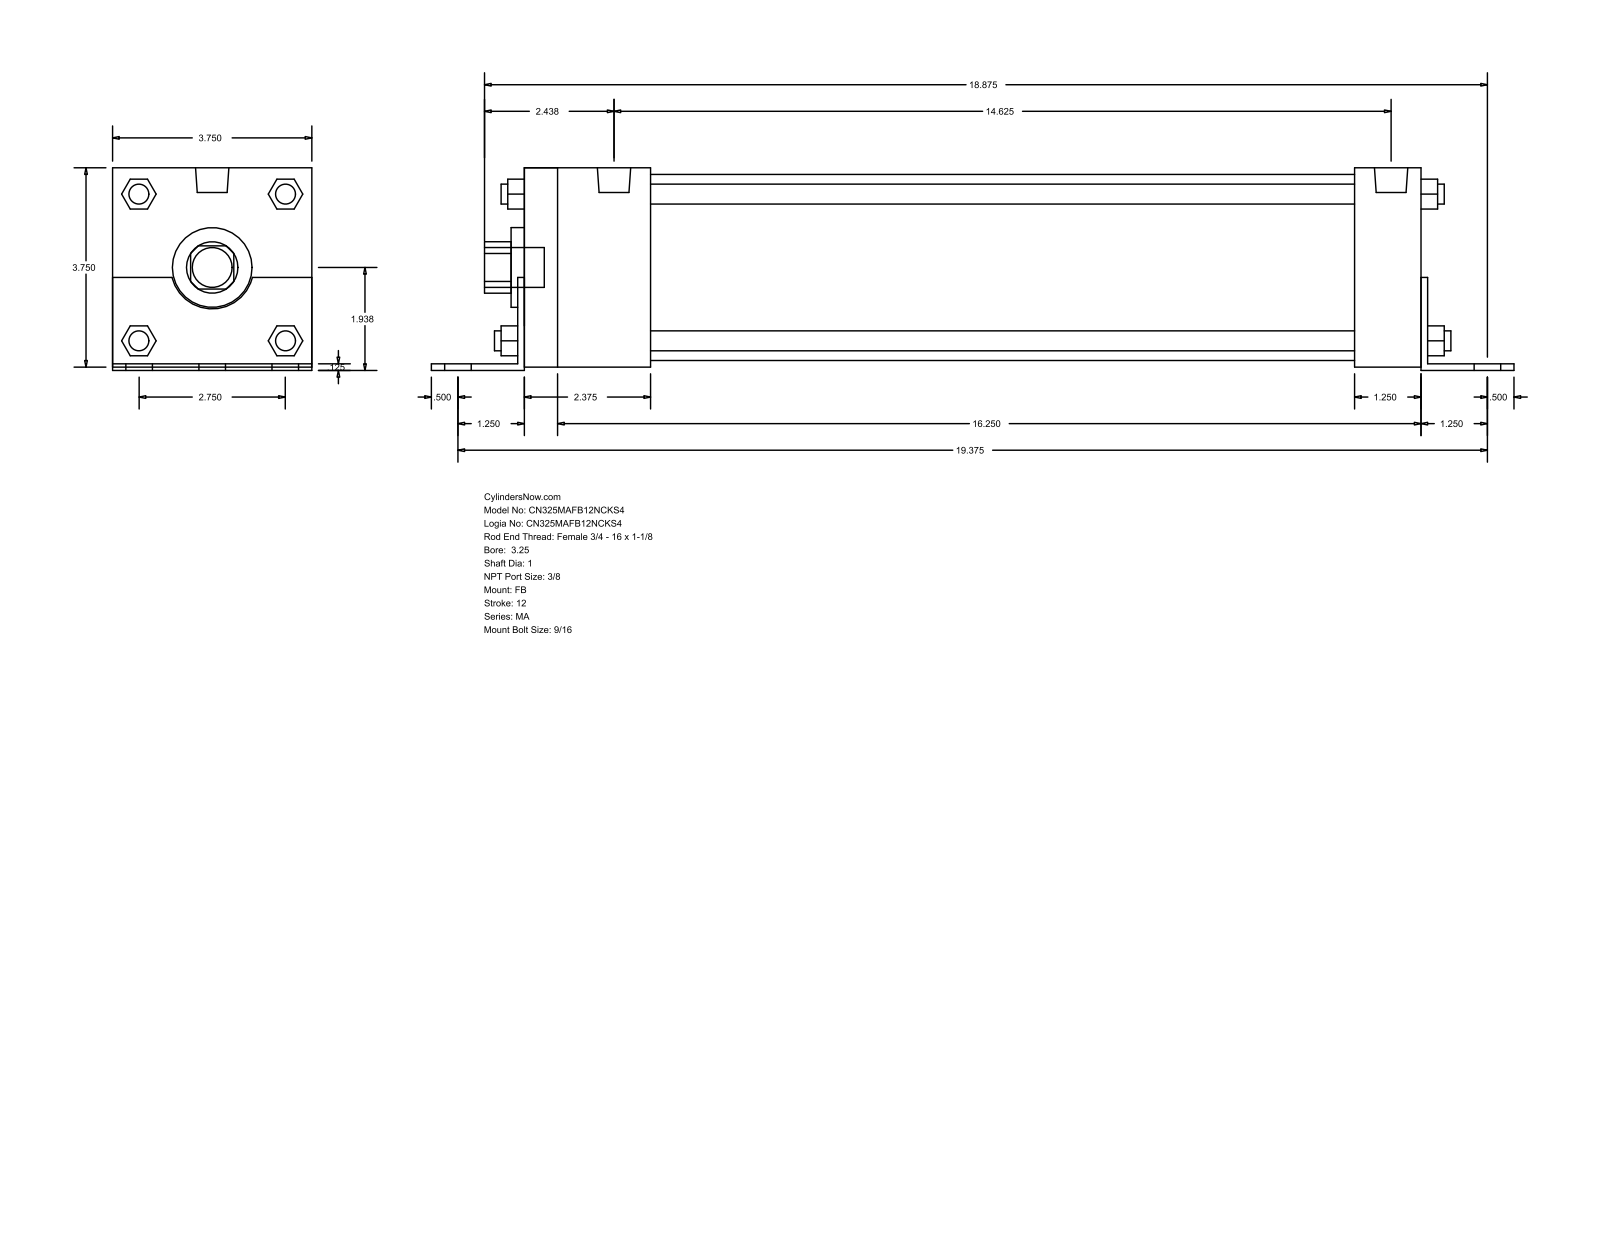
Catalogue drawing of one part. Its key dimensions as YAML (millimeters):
part_name: "MA_FB__0325_1"
step_written_by: "GSSL Pune (CONFIG_CONTROL_DESIGN)"
units: millimeters
bodies: {solids: 0, faces: 140, planar: 105, cylindrical: 35, other: 0}
overall_size: [517.52, 96.84, 95.25]
round_holes:
  - {diameter: 25.4, count: 1}
  - {diameter: 38.1, count: 1}
  - {diameter: 88.9, count: 1}
round_bosses_or_shafts:
  - {diameter: 14.29, count: 6}
  - {diameter: 11.11, count: 4}
  - {diameter: 9.53, count: 4}
  - {diameter: 15.93, count: 2}
  - {diameter: 19.05, count: 1}
partial_cylinders:
  - {radius: 12.29, count: 1}
  - {radius: 19.81, count: 1}
face_to_face_distances: [95.24, 3.17, 1.59, 96.83, 1.58, 93.66, 431.8, 428.63, 434.97, 400.05]
